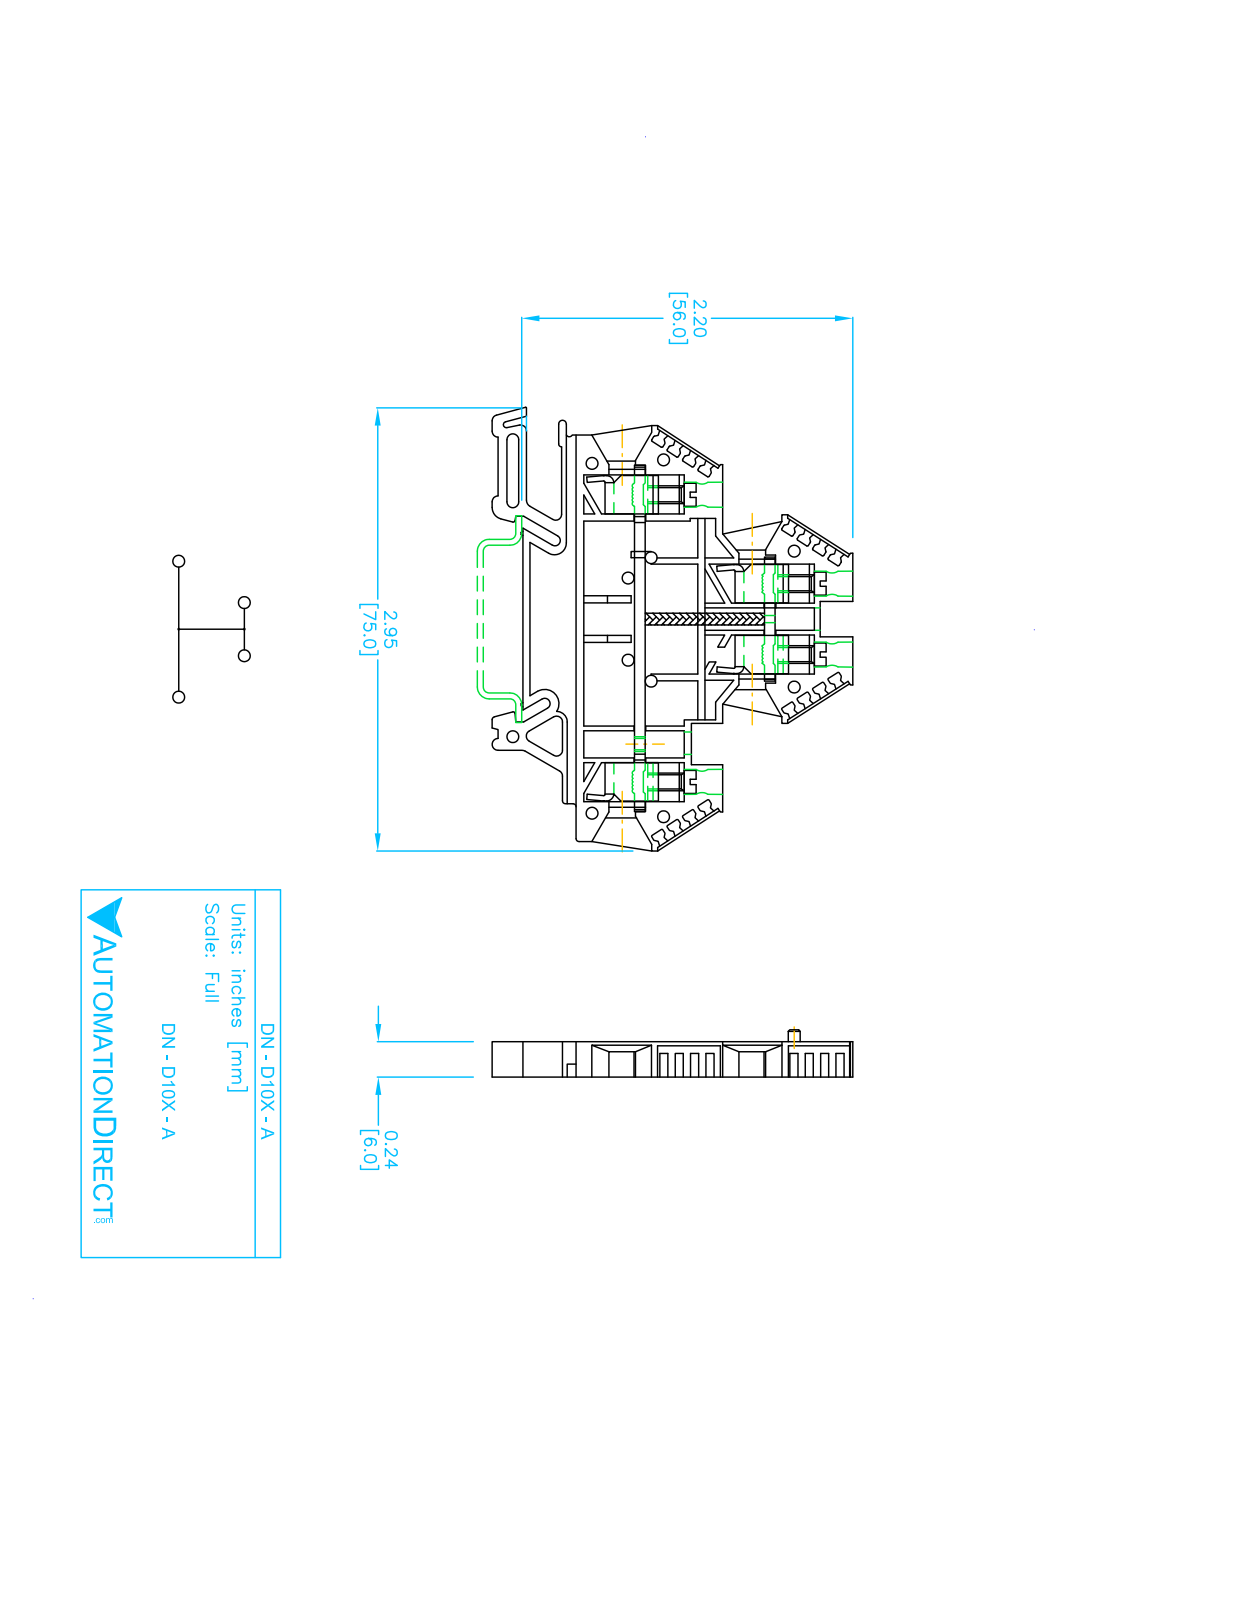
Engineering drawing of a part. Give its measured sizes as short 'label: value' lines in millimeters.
name: DN-D10X-A
written by: SolidWorks 2017 (AUTOMOTIVE_DESIGN)
unit: mm
bodies: 1 solid, 402 faces (261 planar, 141 cylindrical, 0 other)
size: 75.1 × 61 × 6
volume: 14 700 mm³; area: 9 581 mm²
holes: 4× ⌀4.2, 1× ⌀2
bosses: 4× ⌀3.7
rounds: 64× R0.2, 13× R1, 6× R0.5, 2× R0.3, 2× R0.9, 2× R1.9, 2× R2, 1× R0.1
face distances: 6, 2, 4, 9, 1.5, 0.6, 0.8, 1.2, 24.8, 1.8
hole spacings: 12, 15.1, 21.5, 27.1, 33.6, 48.6
